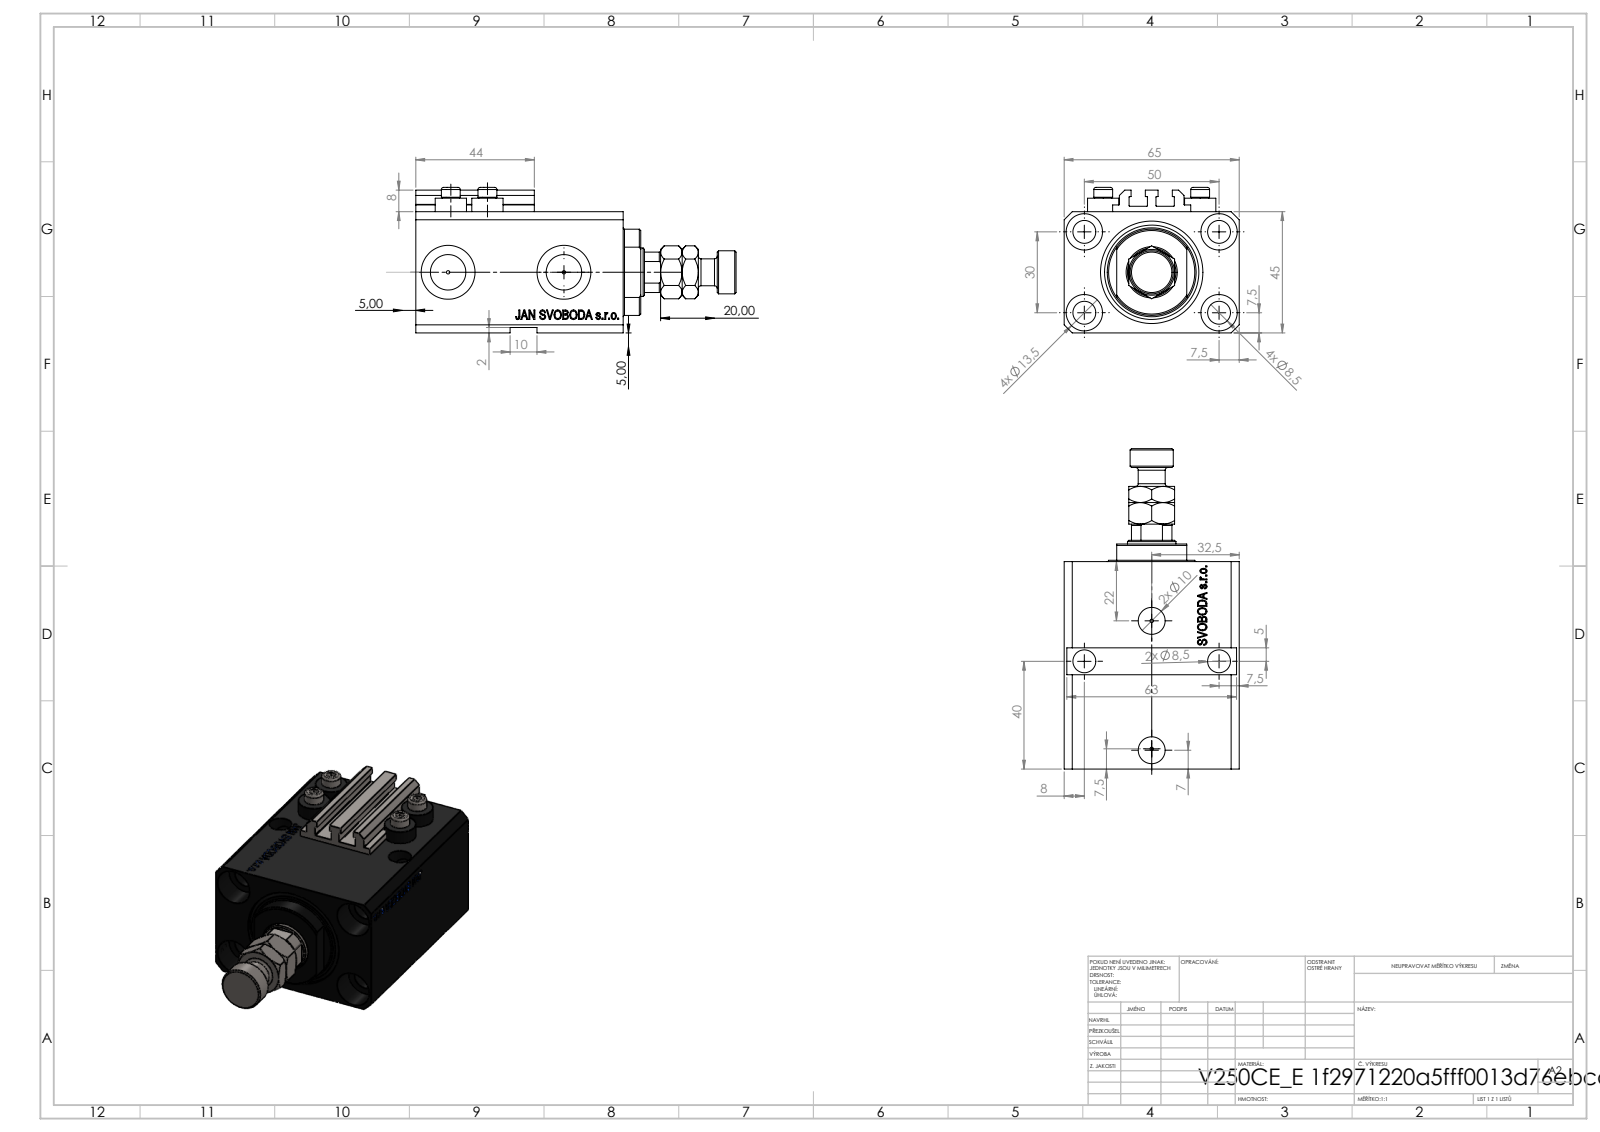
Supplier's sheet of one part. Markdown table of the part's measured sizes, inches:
| quantity | value |
| --- | --- |
| part name | V250CE_C_VCP; V250CE_VC_E; ALLEN BOLT V250CE; MFA (+1 more) |
| STEP written by | SolidWorks 2019 (CONFIG_CONTROL_DESIGN) |
| units | inches |
| bodies | 9 solids, 1119 faces (527 planar, 130 cylindrical, 462 other) |
| overall size | 4.685 × 2.559 × 2.126 |
| volume | 12.52 in³ |
| surface area | 94.94 in² |
| round holes (diameter × count) | 0.335 × 7, 0.049 × 4, 0.157 × 4, 0.531 × 4, 0.394 × 2, 0.518 × 2, 0.787 × 2, 0.709 × 1, 0.984 × 1, 1.496 × 1 |
| round bosses / shafts (diameter × count) | 0.457 × 4, 0.276 × 4, 0.63 × 1, 0.394 × 1 |
| partial cylindrical surfaces (radius × count) | 0.008 × 10, 0.335 × 1, 0.63 × 1 |
| main face-to-face distances | 1.772, 2.559, 0.551, 2.48, 3.031, 0.079, 0.272, 2.209, 2.76, 0.807 |
| hole center spacings | 1.148, 1.969, 0.535, 0.595, 0.741, 0.747, 1.032, 1.048 |
